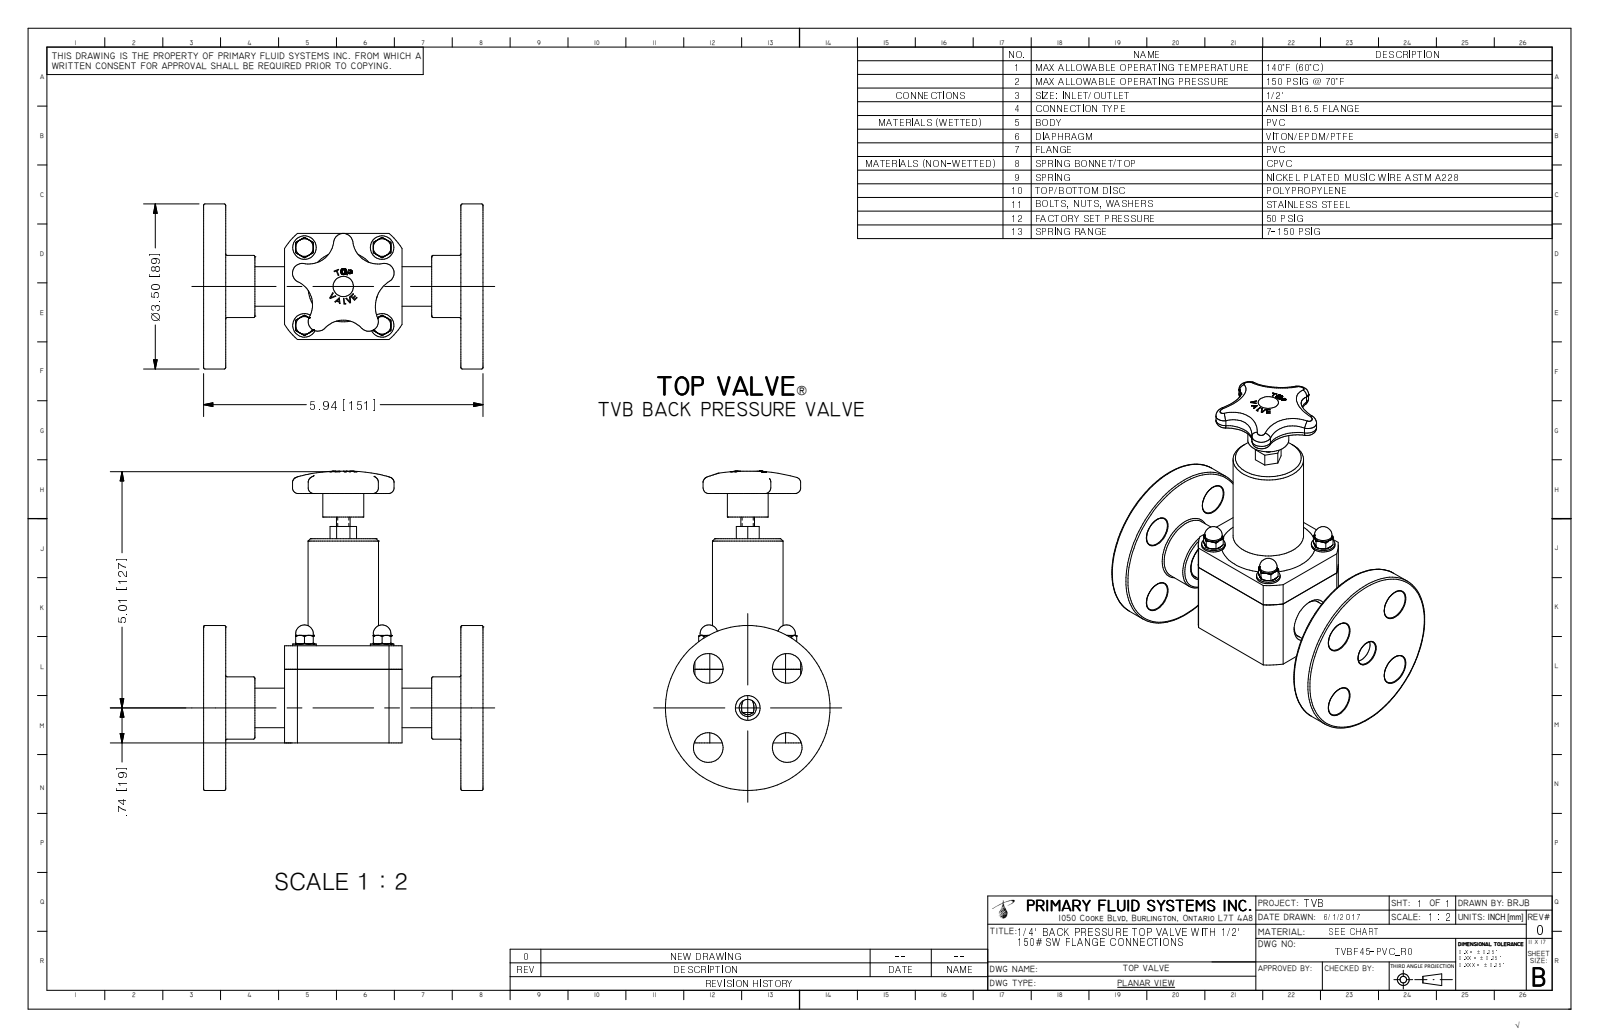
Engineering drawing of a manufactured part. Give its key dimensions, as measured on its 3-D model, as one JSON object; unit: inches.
{"part_name": "TVBF45-PVC_R0", "step_written_by": "Autodesk Inventor 2009 (AUTOMOTIVE_DESIGN)", "units": "inches", "bodies": {"solids": 1, "faces": 393, "planar": 148, "cylindrical": 57, "other": 188}, "overall_size": [6.772, 5.94, 3.5], "volume_in3": 25.82, "surface_area_in2": 128.7, "round_holes": [[0.147, 4], [0.63, 4], [0.526, 1]], "round_bosses_or_shafts": [[0.5, 4], [0.375, 4], [0.312, 4], [3.5, 1], [1.5, 1], [1.32, 1], [0.87, 1], [0.293, 1]], "partial_cylinders_radius": [[0.085, 5], [0.205, 5], [0.536, 4], [0.656, 4], [0.625, 1], [0.745, 1], [1.488, 1]], "face_to_face_distances": [0.47, 5.47, 5.94, 5, 4.22, 1.72, 1.25, 3.75, 2.25, 2.5], "hole_center_spacings": [1.65, 1.187, 1.188, 1.679, 1.68, 2.334, 2.375]}
